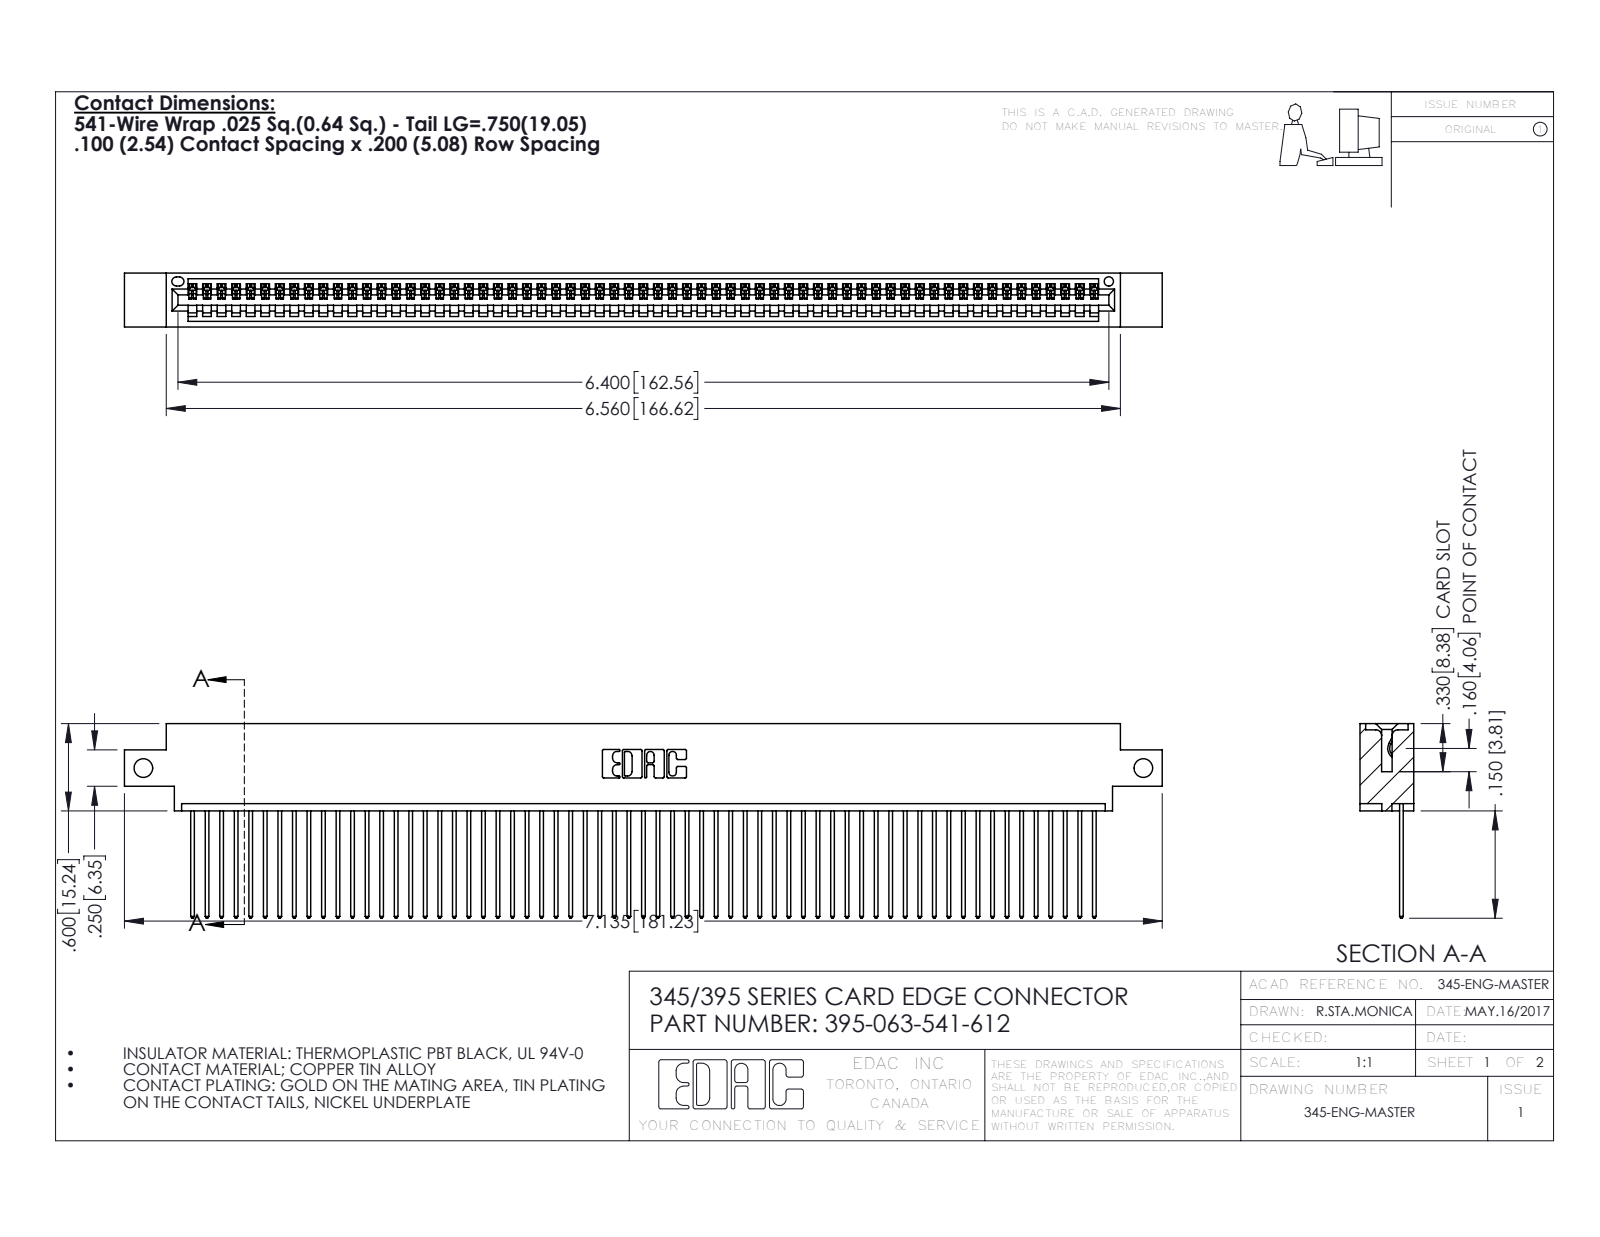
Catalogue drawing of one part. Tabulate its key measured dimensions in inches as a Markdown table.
| quantity | value |
| --- | --- |
| part name | 345-292-001_345-293-141; 345 Part_0.170 Offset - Side Mount; 395-063-541-612 |
| STEP written by | SolidWorks 2016 (CONFIG_CONTROL_DESIGN) |
| units | inches |
| bodies | 64 solids, 3784 faces (2604 planar, 1180 cylindrical, 0 other) |
| overall size | 7.135 × 1.337 × 0.37 |
| volume | 1.061 in³ |
| surface area | 38.14 in² |
| round holes (diameter × count) | 0.128 × 2, 0.064 × 1 |
| partial cylindrical surfaces (radius × count) | 0.006 × 126, 0.01 × 126, 0.01 × 22, 0.007 × 6, 0.031 × 6, 0.026 × 3, 0.031 × 2, 0.04 × 2 |
| main face-to-face distances | 0.072, 0.298, 0.098, 0.272, 0.025, 0.37, 0.2, 0.225, 0.175, 0.149 |
| hole center spacings | 6.875 |
